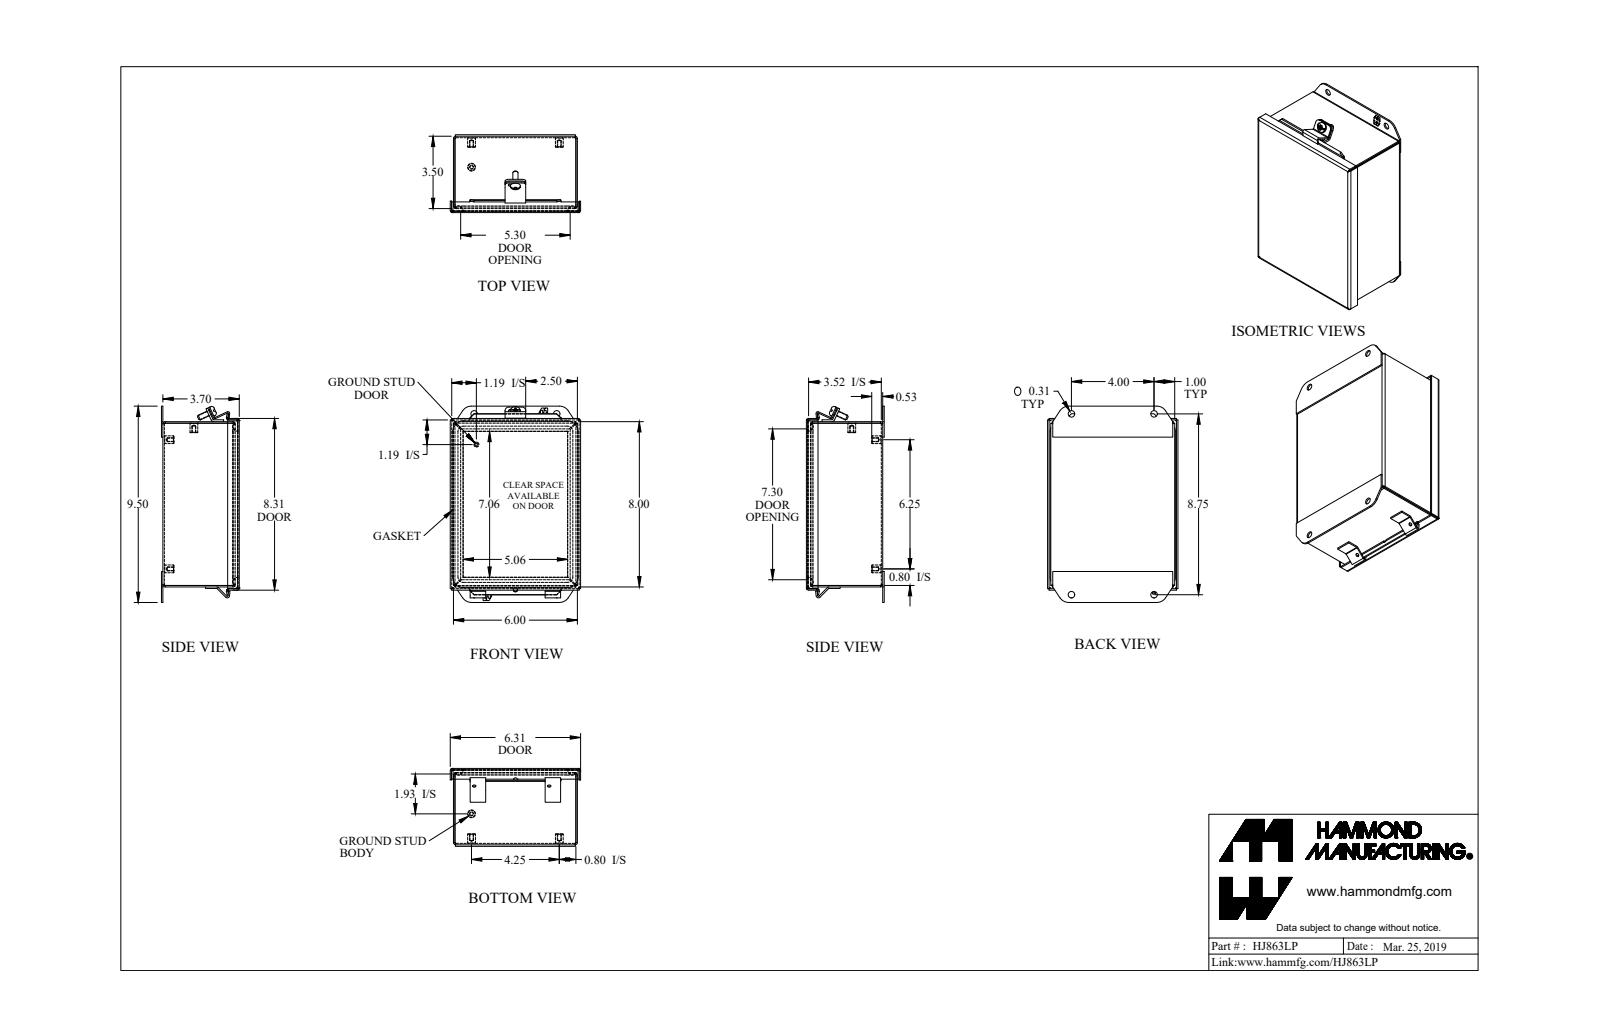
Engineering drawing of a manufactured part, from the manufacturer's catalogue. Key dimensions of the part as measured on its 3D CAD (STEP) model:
Part name (STEP PRODUCT): HJ863LP
STEP written by: SolidWorks 2018 (AUTOMOTIVE_DESIGN)
Units: inches
Bodies: 16 solids, 518 faces (282 planar, 136 cylindrical, 100 other)
Overall size (bounding box): 9.5 × 6.312 × 3.769
Volume: 19.82 in³ · Surface area: 548.1 in²
Round holes (diameter × count): ⌀0.156 ×5, ⌀0.313 ×4, ⌀0.156 ×2, ⌀0.213 ×1
Round bosses / shafts (diameter × count): ⌀0.375 ×5, ⌀0.25 ×2, ⌀0.48 ×1, ⌀0.188 ×1
Partial cylindrical surfaces — rounded edges, fillets, slot ends (radius × count): R0.036 ×16, R0.108 ×16, R0.25 ×16, R0.499 ×4, R0.5 ×4, R0.01 ×2, R0.029 ×2, R0.086 ×2
Main face-to-face distances: 0.072, 3.625, 3.697, 5.928, 3.553, 7.928, 5.856, 6, 0.156, 8
Hole centre spacings: 1.256, 4.31, 7.501, 8.559, 4, 4.25, 6.25, 7.558
